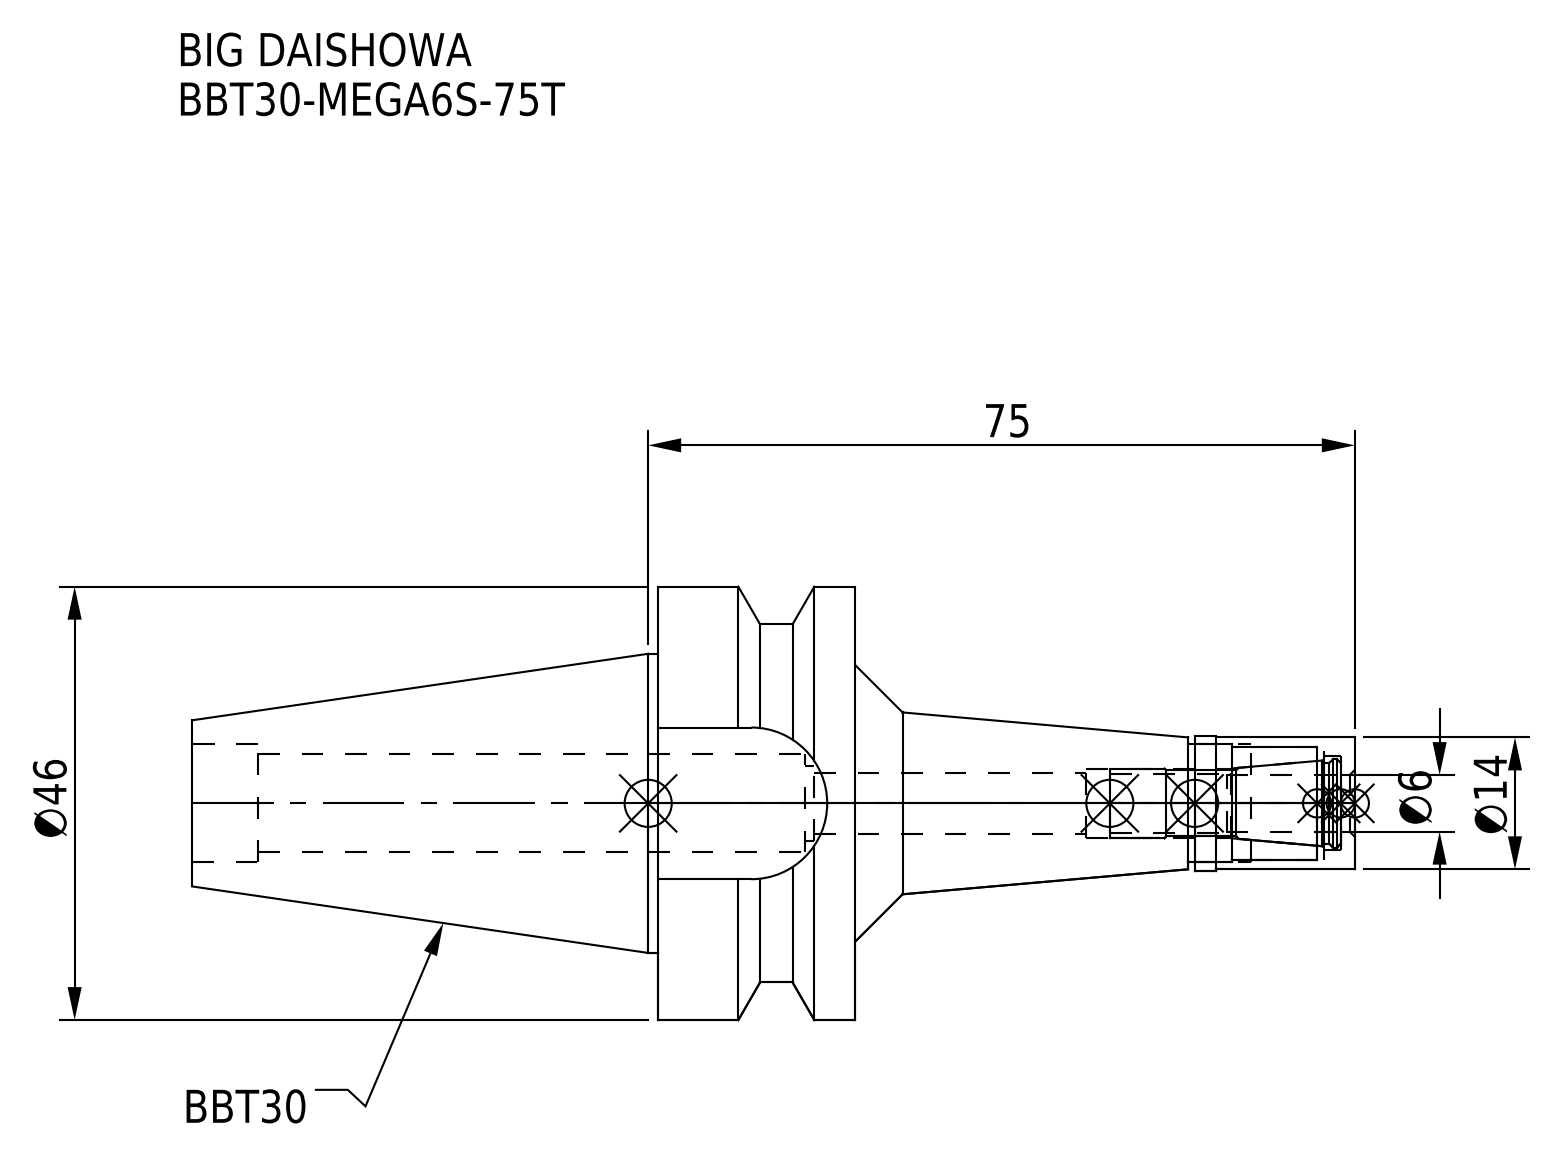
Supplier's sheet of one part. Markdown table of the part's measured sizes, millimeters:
| quantity | value |
| --- | --- |
| part name | MGN6S_1.stp; DXF_TEMP_ASSY_ASM_4_ASM.stp; BBT30-MEGA6S-75T_1.stp; BBT30-MEGA6S-75T.stp (+3 more) |
| STEP written by | SolidWorks 2019 (CONFIG_CONTROL_DESIGN) |
| units | millimeters |
| bodies | 2 solids, 74 faces (22 planar, 38 cylindrical, 14 other) |
| overall size | 123.4 × 46 × 46 |
| volume | 57 357 mm³ |
| surface area | 17 267 mm² |
| round holes (diameter × count) | 6.1 × 1, 6.4 × 1, 7.4 × 1, 8 × 1, 10 × 1, 10.4 × 1, 12 × 1, 12.5 × 1 |
| round bosses / shafts (diameter × count) | 46 × 1, 31.75 × 1, 14.3 × 1, 14 × 1 |
| partial cylindrical surfaces (radius × count) | 8.05 × 1, 19 × 1 |
| main face-to-face distances | 21, 32.6, 70.4, 49.4, 53, 74, 123.4, 16.1, 0.7, 13.7 |
